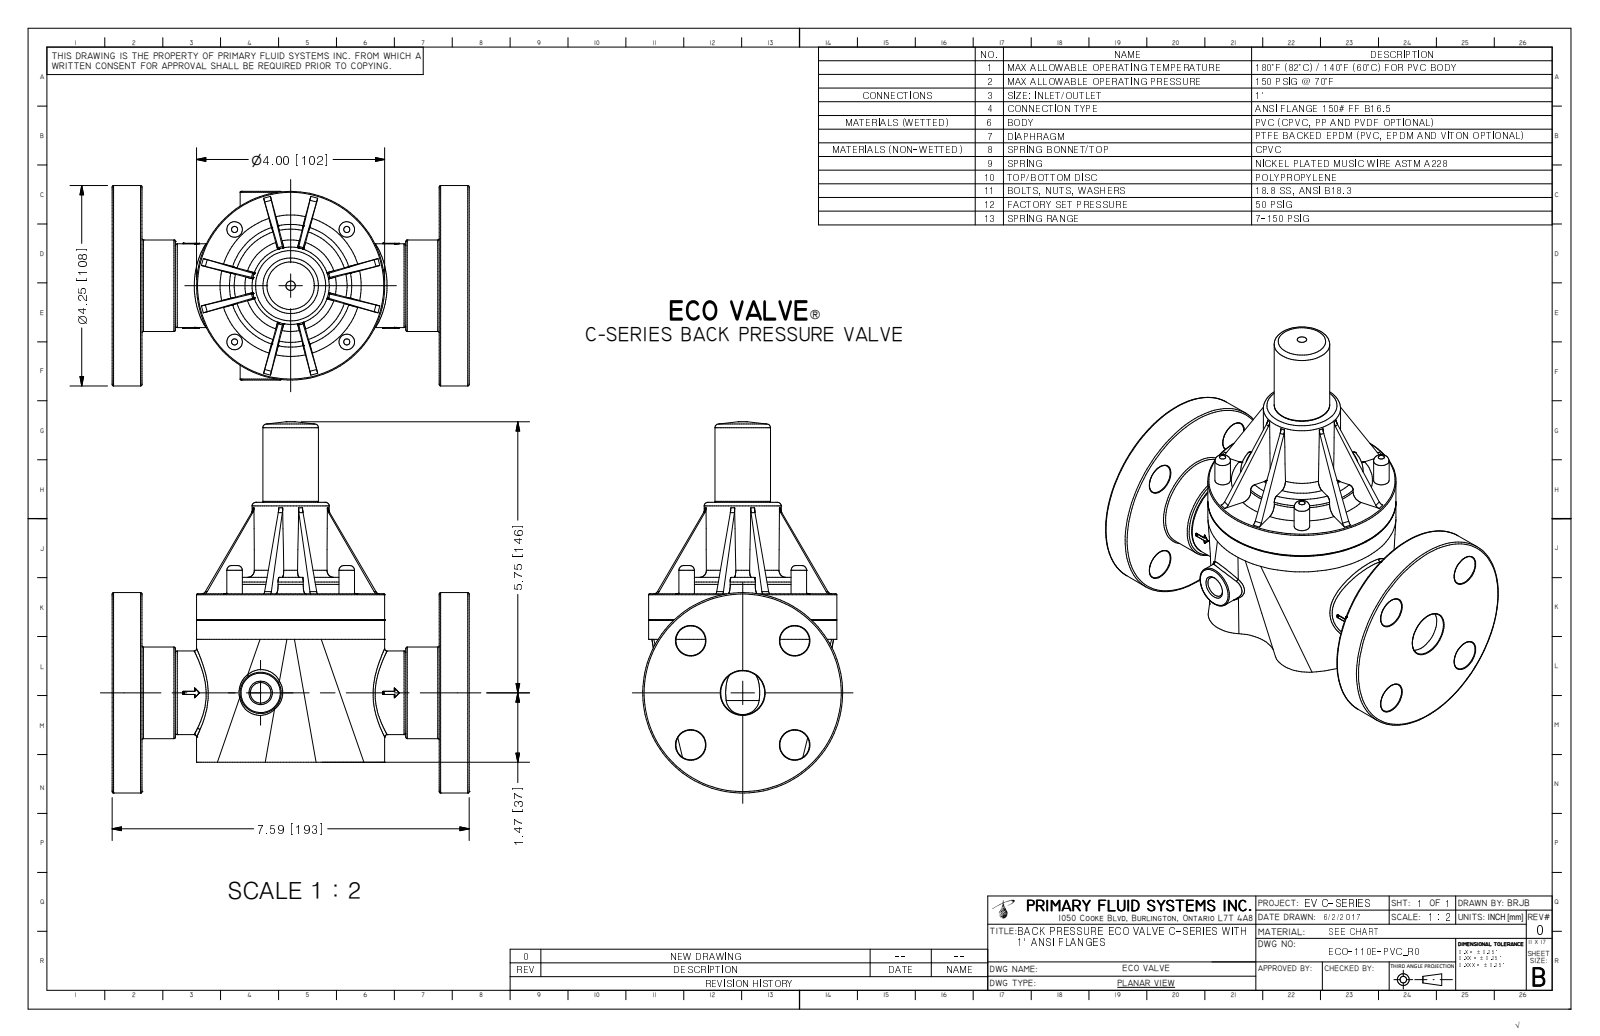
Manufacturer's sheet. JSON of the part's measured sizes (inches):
{"part_name": "ECO-110E-PVC_R0", "step_written_by": "Autodesk Inventor 2009 (AUTOMOTIVE_DESIGN)", "units": "inches", "bodies": {"solids": 1, "faces": 440, "planar": 167, "cylindrical": 89, "other": 184}, "overall_size": [7.874, 7.59, 4.25], "volume_in3": 64.6, "surface_area_in2": 261.1, "round_holes": [[0.23, 4], [0.63, 4], [0.437, 1], [0.936, 1], [0.957, 1]], "round_bosses_or_shafts": [[0.4, 4], [0.33, 4], [4.25, 1], [4, 1], [2.6, 1], [1.941, 1], [1.775, 1], [1.64, 1]], "partial_cylinders_radius": [[0.1, 14], [0.05, 4], [0.225, 4], [0.15, 1], [0.898, 1], [1.559, 1], [1.816, 1]], "face_to_face_distances": [0.635, 6.955, 7.59, 6.32, 3.572, 0.45, 3.122, 3.007, 2.557, 0.565], "hole_center_spacings": [2.385, 1.562, 1.563, 2.209, 2.21, 3.125, 3.373]}
